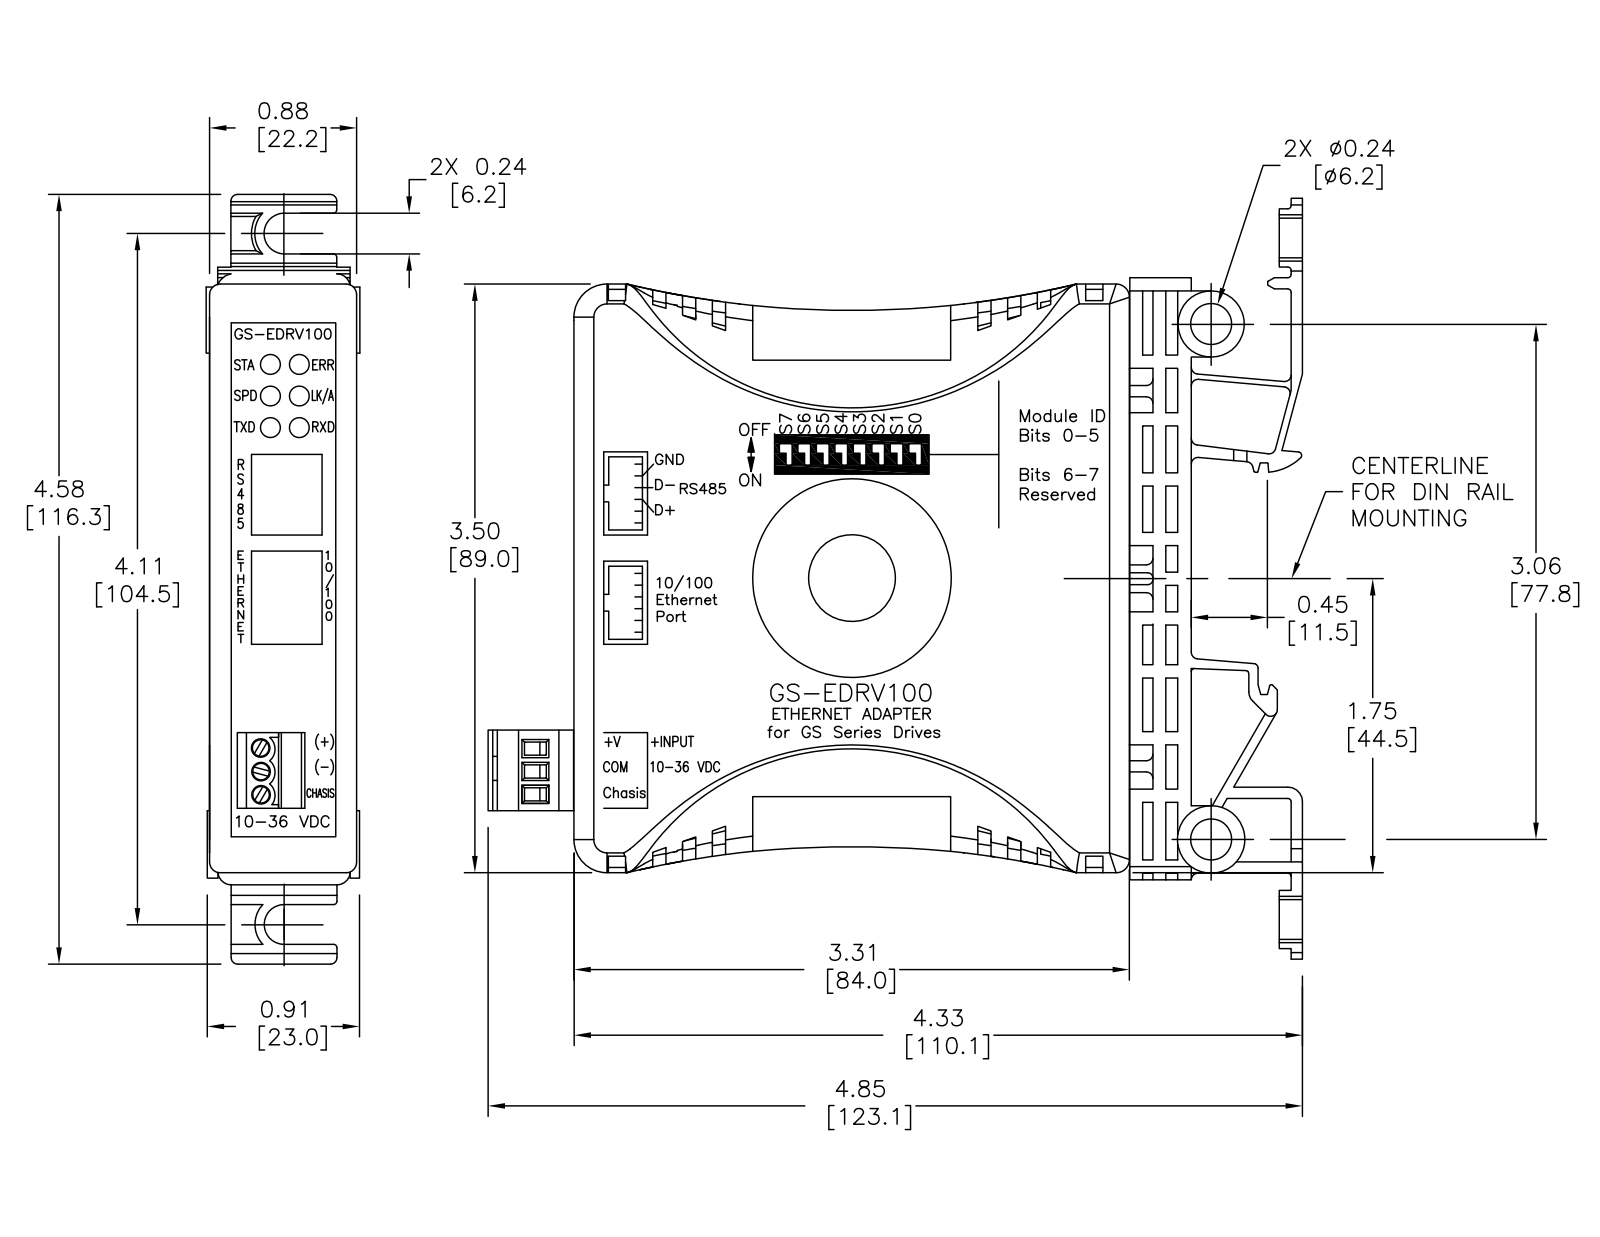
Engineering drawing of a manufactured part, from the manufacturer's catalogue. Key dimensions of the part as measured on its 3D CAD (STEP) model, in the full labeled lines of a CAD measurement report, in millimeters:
Part name (STEP PRODUCT): GS-EDRV100; GS-EDRV100 DIN rail bracket
STEP written by: SolidWorks 2009 (AUTOMOTIVE_DESIGN)
Units: millimetres
Bodies: 7 solids, 841 faces (669 planar, 121 cylindrical, 51 other)
Overall size (bounding box): 118.6 × 115.5 × 26.7
Volume: 169 000 mm³ · Surface area: 43 010 mm²
Round holes (diameter × count): ⌀3 ×3, ⌀6.2 ×2
Round bosses / shafts (diameter × count): ⌀2.7 ×6, ⌀10.2 ×1, ⌀10 ×1
Partial cylindrical surfaces — rounded edges, fillets, slot ends (radius × count): R2.5 ×10, R1 ×8, R0.3 ×6, R0.5 ×5, R2 ×4, R73.3 ×4, R0.1 ×2, R0.3 ×2
Main face-to-face distances: 23.1, 3.5, 2, 3.8, 7.2, 5.5, 1.8, 91.3, 89.5, 87.6
Hole centre spacings: 3.6, 3.6, 7.1, 77.9, 99.9, 100.4, 100.9, 116.4
